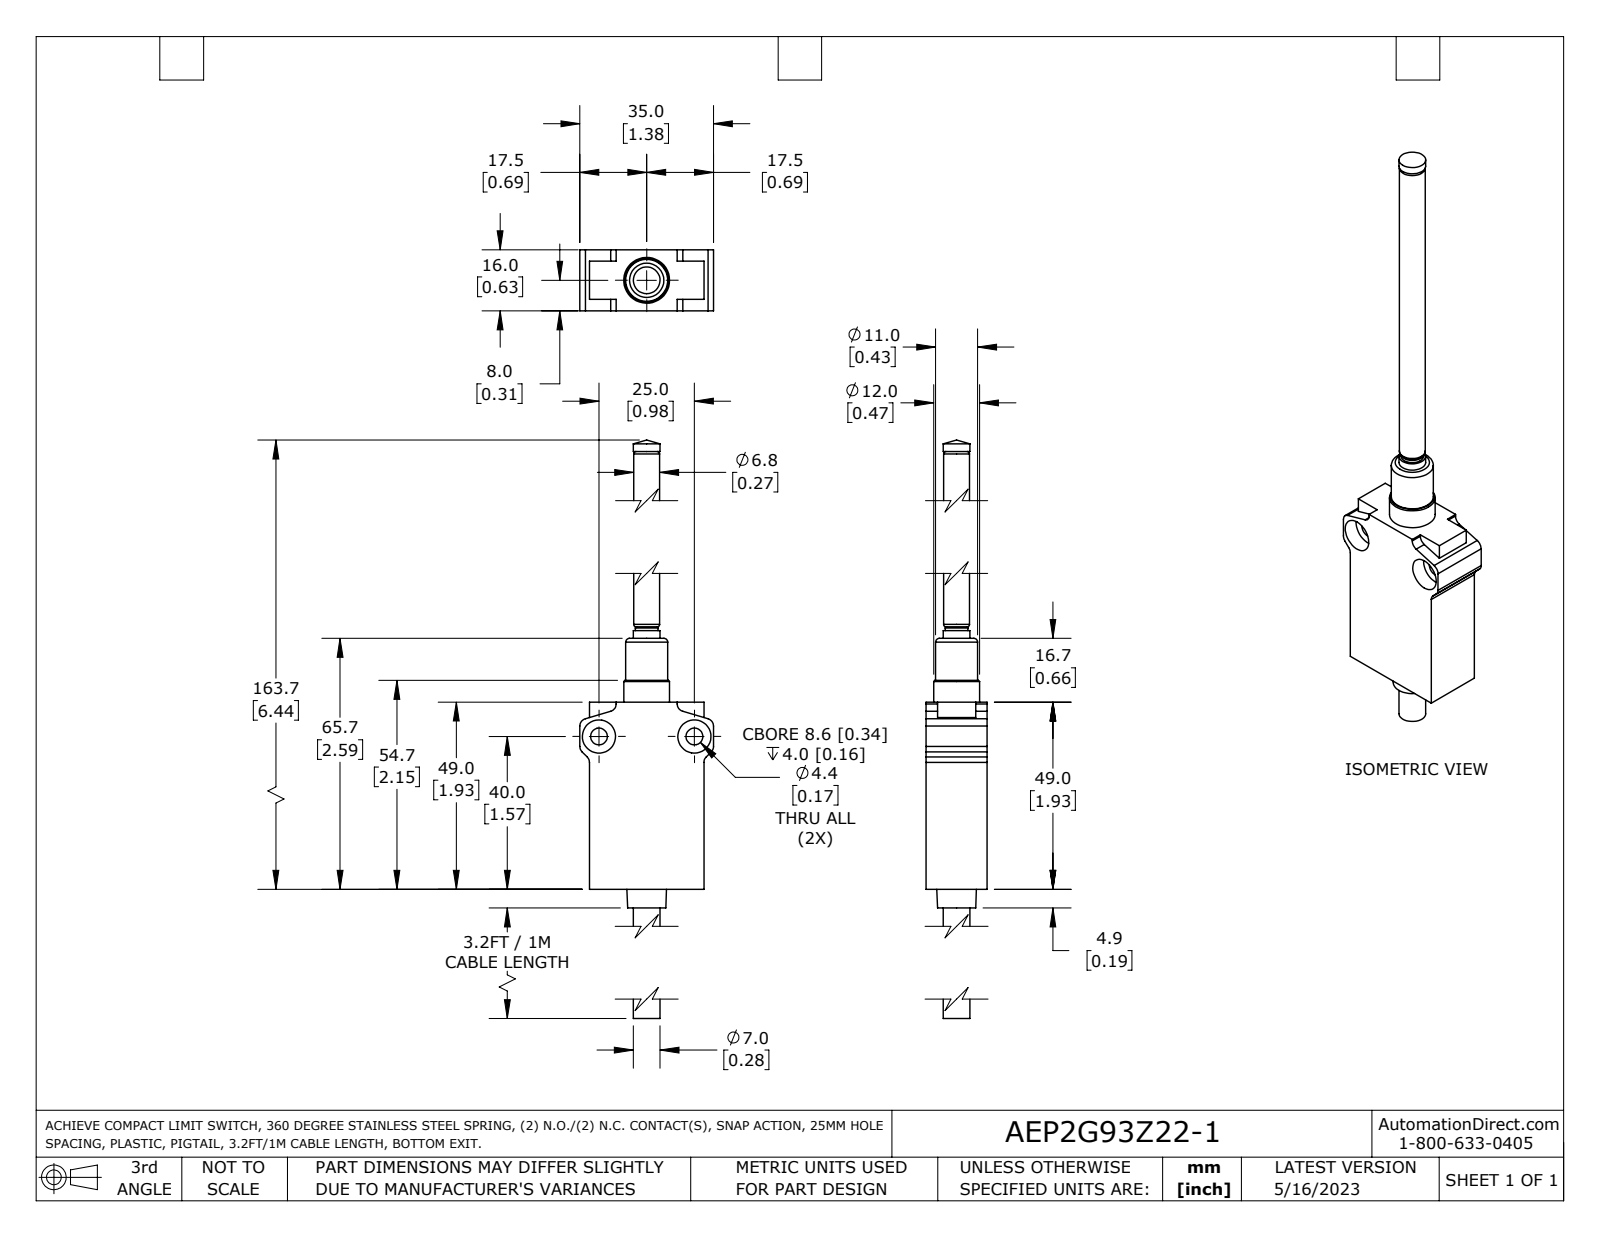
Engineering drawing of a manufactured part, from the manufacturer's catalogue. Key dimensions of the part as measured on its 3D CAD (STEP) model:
Part name (STEP PRODUCT): AEP2G93Z22-1
STEP written by: SolidWorks 2021 (AUTOMOTIVE_DESIGN)
Units: inches
Bodies: 1 solid, 83 faces (45 planar, 27 cylindrical, 11 other)
Overall size (bounding box): 7.031 × 1.378 × 0.63
Volume: 1.758 in³ · Surface area: 14.4 in²
Round holes (diameter × count): ⌀0.173 ×2, ⌀0.343 ×2
Round bosses / shafts (diameter × count): ⌀0.472 ×1, ⌀0.433 ×1, ⌀0.276 ×1, ⌀0.268 ×1, ⌀0.232 ×1
Partial cylindrical surfaces — rounded edges, fillets, slot ends (radius × count): R0.079 ×8, R0.256 ×1
Main face-to-face distances: 0.63, 1.181, 1.929, 0.472, 0.157, 0.098, 1.28, 0.512, 0.315, 1.378
Hole centre spacings: 0.984
